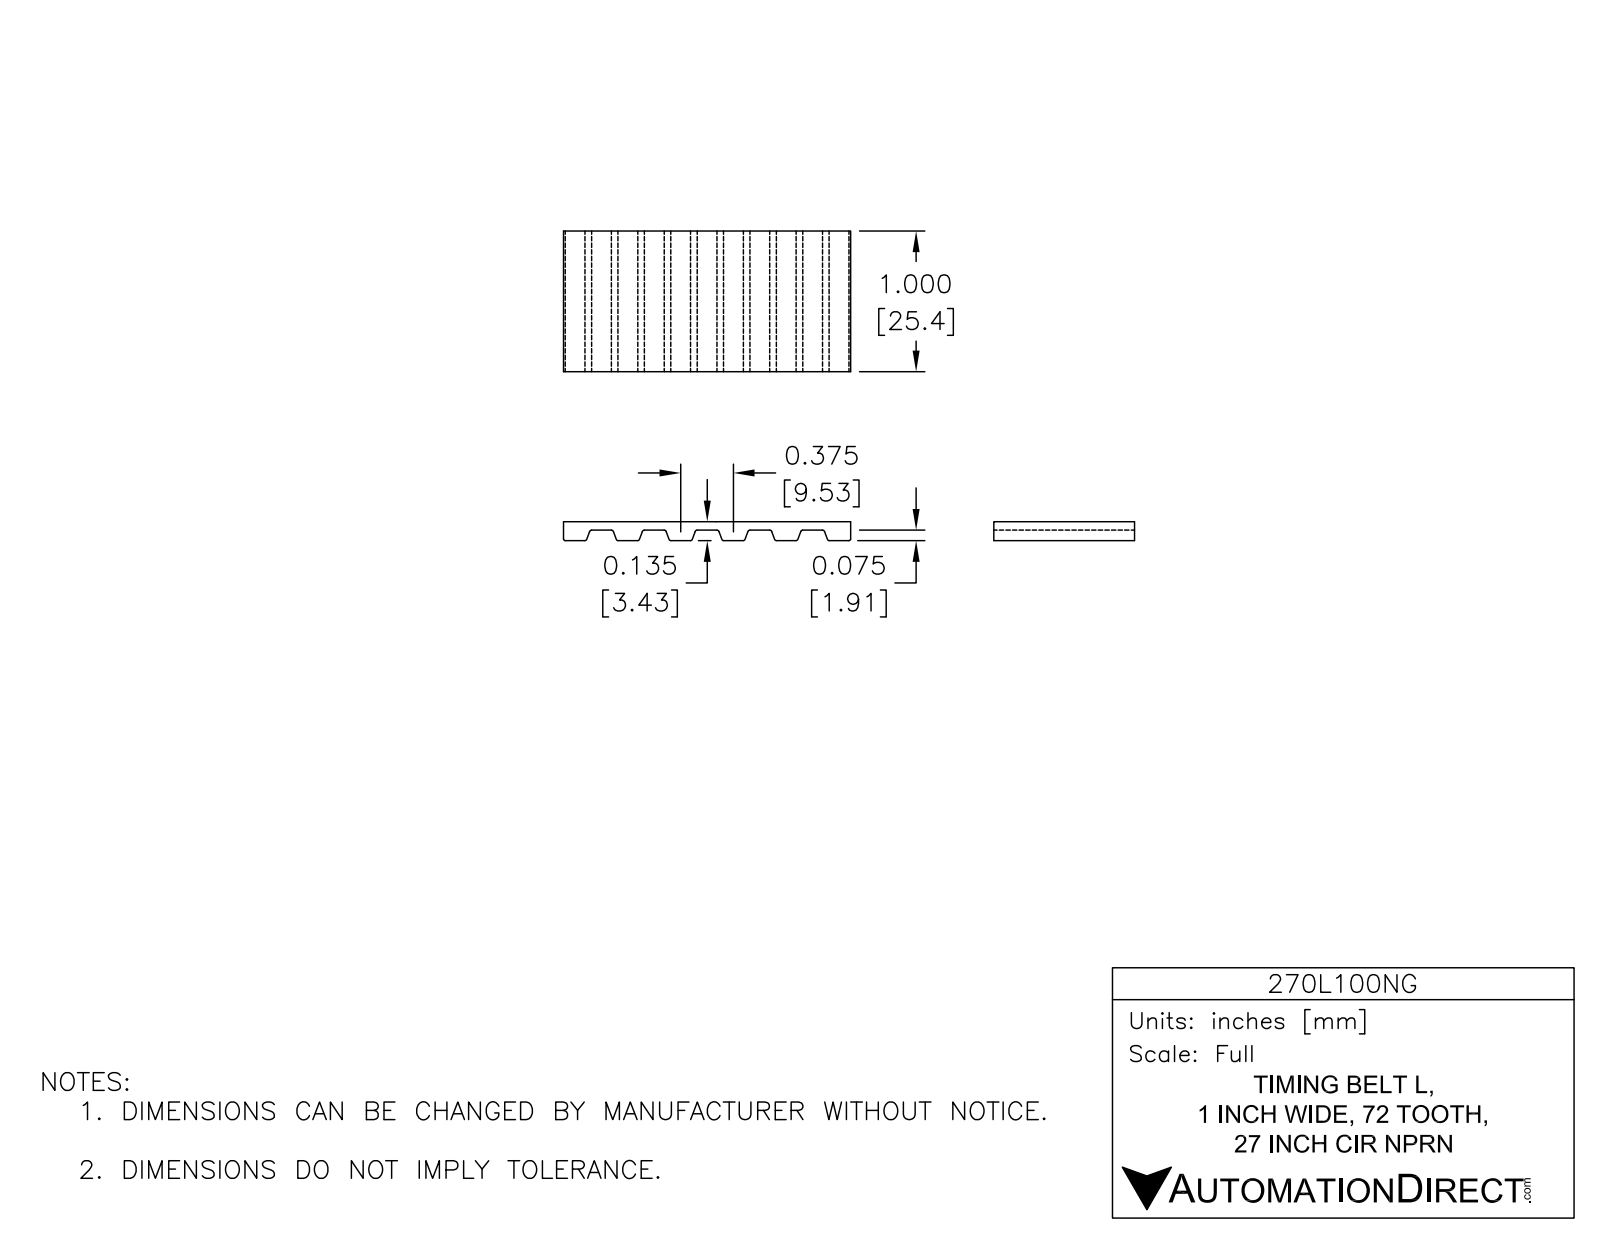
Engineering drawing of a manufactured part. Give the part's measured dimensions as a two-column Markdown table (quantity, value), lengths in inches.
| quantity | value |
| --- | --- |
| part name | 270L100NG |
| STEP written by | SolidWorks 2014 (AUTOMOTIVE_DESIGN) |
| units | inches |
| bodies | 1 solid, 591 faces (265 planar, 326 cylindrical, 0 other) |
| overall size | 11.788 × 3 × 1 |
| volume | 2.438 in³ |
| surface area | 64.89 in² |
| partial cylindrical surfaces (radius × count) | 0.02 × 284, 1.435 × 2, 1.5 × 2 |
| main face-to-face distances | 0.065, 2.935, 3, 2.87, 0.14, 2.86, 0.075, 2.795, 1, 2.72 |
